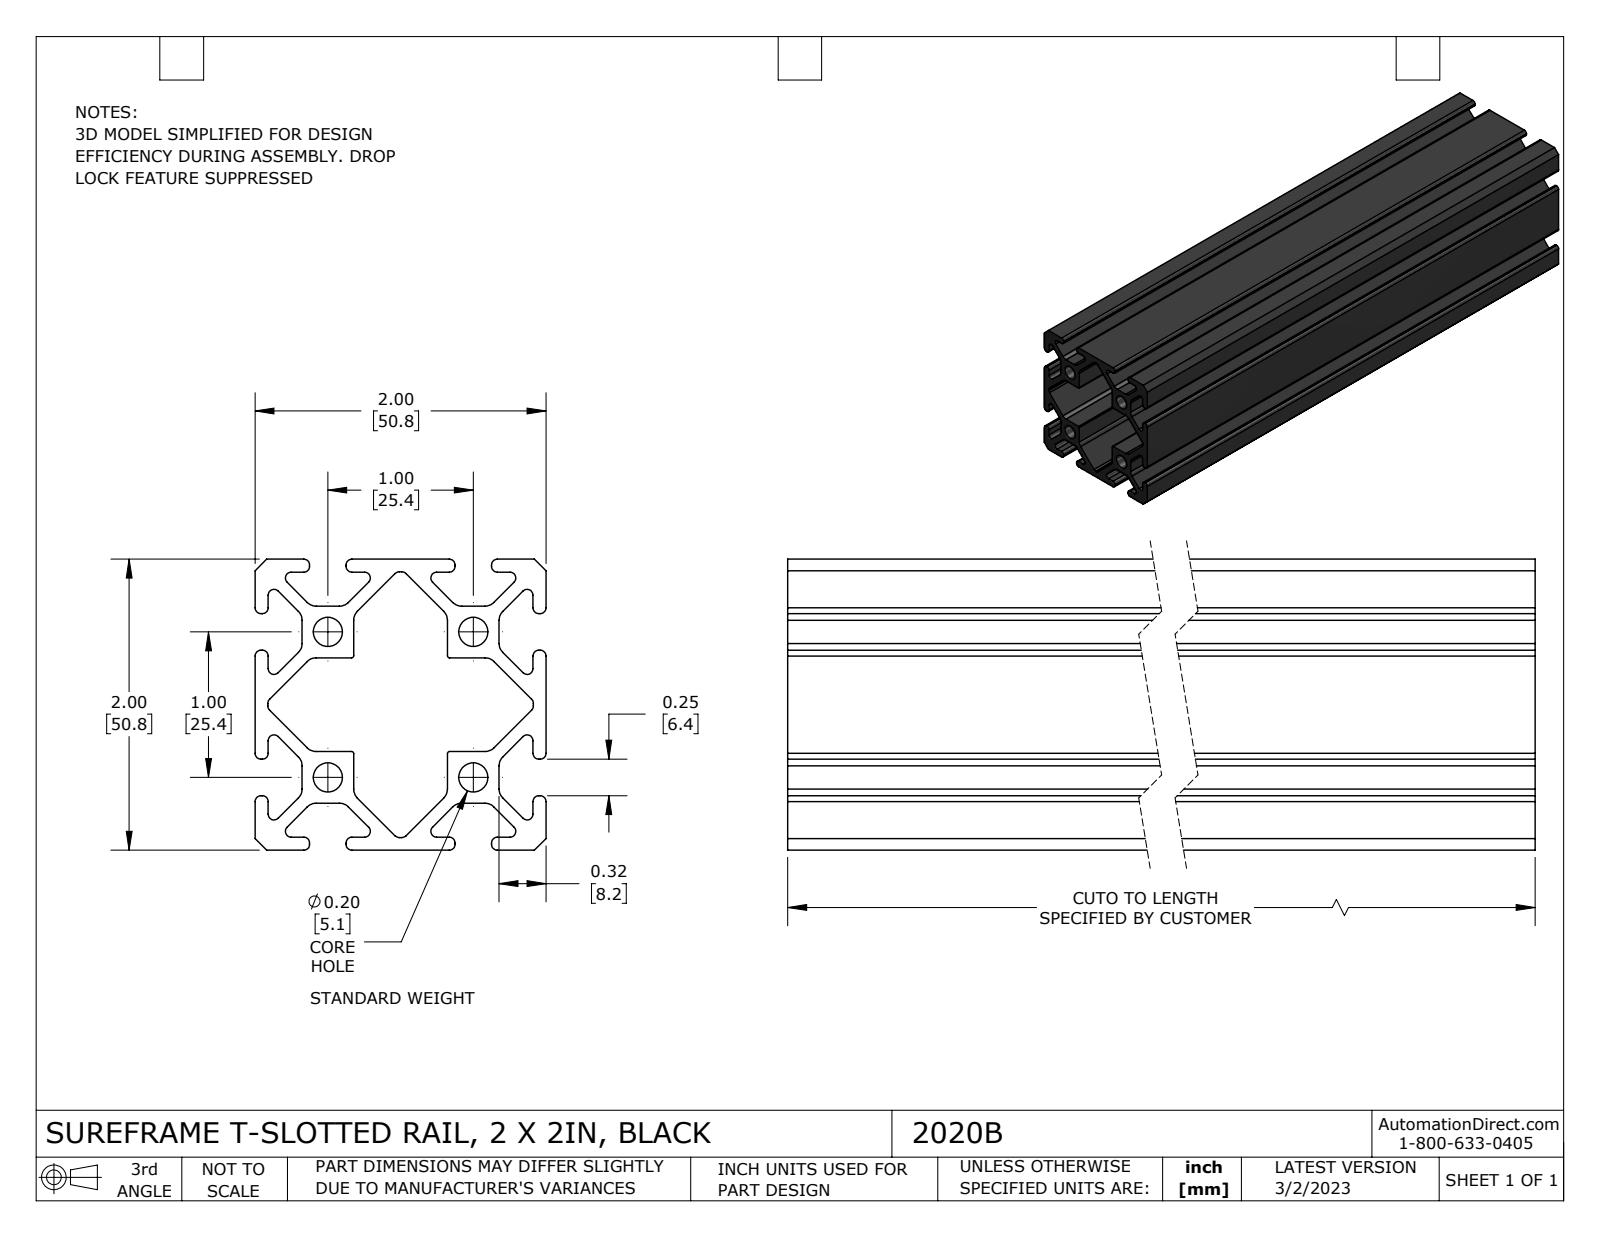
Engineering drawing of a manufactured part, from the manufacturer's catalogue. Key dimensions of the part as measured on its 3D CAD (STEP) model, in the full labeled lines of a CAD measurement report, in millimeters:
Part name (STEP PRODUCT): 2020B
STEP written by: SolidWorks 2021 (CONFIG_CONTROL_DESIGN)
Units: millimetres
Bodies: 1 solid, 194 faces (94 planar, 100 cylindrical, 0 other)
Overall size (bounding box): 203.2 × 50.8 × 50.8
Volume: 164 200 mm³ · Surface area: 126 100 mm²
Round holes (diameter × count): ⌀5.1 ×4
Partial cylindrical surfaces — rounded edges, fillets, slot ends (radius × count): R1 ×48, R2.2 ×24, R1.1 ×8, R0.4 ×4
Main face-to-face distances: 50.8, 17.2, 33.6, 2.2, 35.9, 18, 20.2, 15.7, 18, 33.7
Hole centre spacings: 25.4, 35.9
